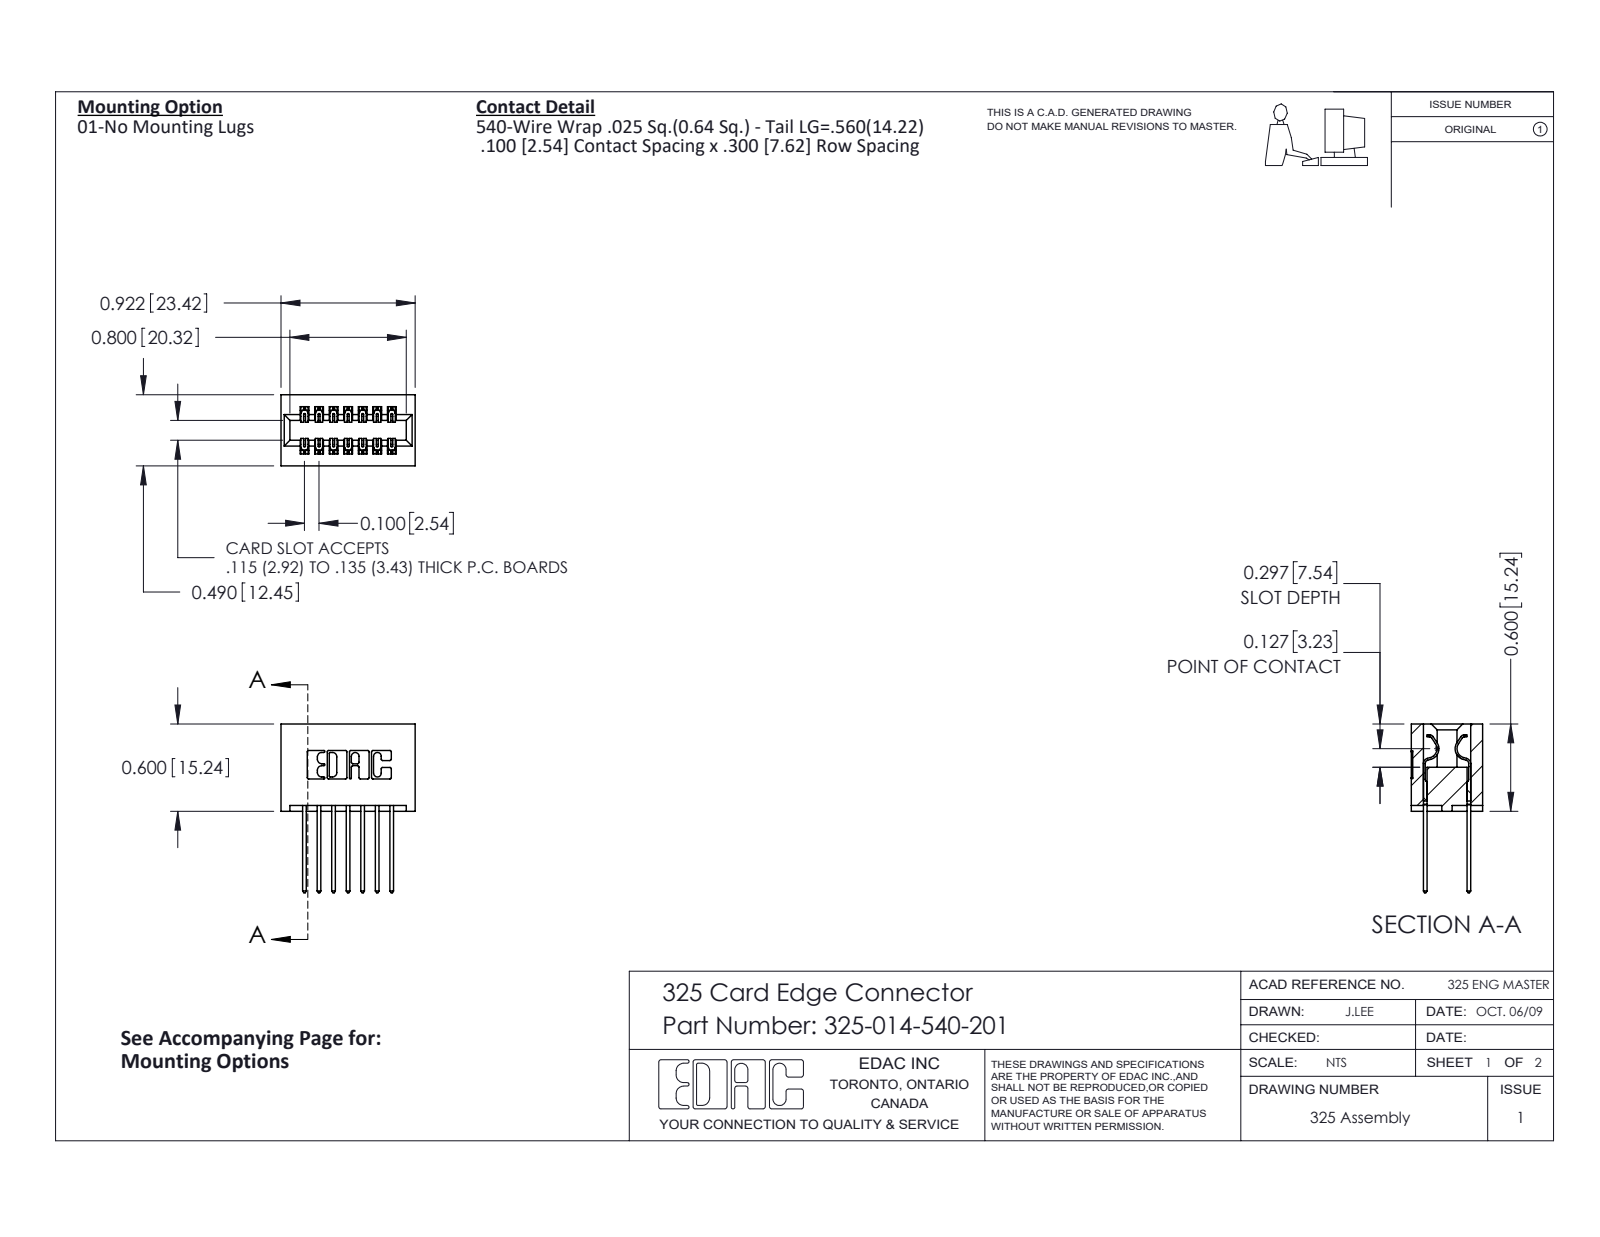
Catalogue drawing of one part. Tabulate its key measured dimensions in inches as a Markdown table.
| quantity | value |
| --- | --- |
| part name | 325 Part_Lugless; 325-014-540-201; 325-292-001_325-293-140 |
| STEP written by | SolidWorks 2016 (CONFIG_CONTROL_DESIGN) |
| units | inches |
| bodies | 15 solids, 834 faces (570 planar, 264 cylindrical, 0 other) |
| overall size | 1.16 × 0.922 × 0.49 |
| volume | 0.206 in³ |
| surface area | 6.449 in² |
| partial cylindrical surfaces (radius × count) | 0.01 × 22, 0.006 × 21, 0.01 × 14, 0.007 × 6, 0.031 × 6, 0.026 × 3, 0.014 × 2, 0.022 × 2 |
| main face-to-face distances | 0.3, 0.083, 0.407, 0.1, 0.2, 0.383, 0.107, 0.025, 0.04, 0.06 |
